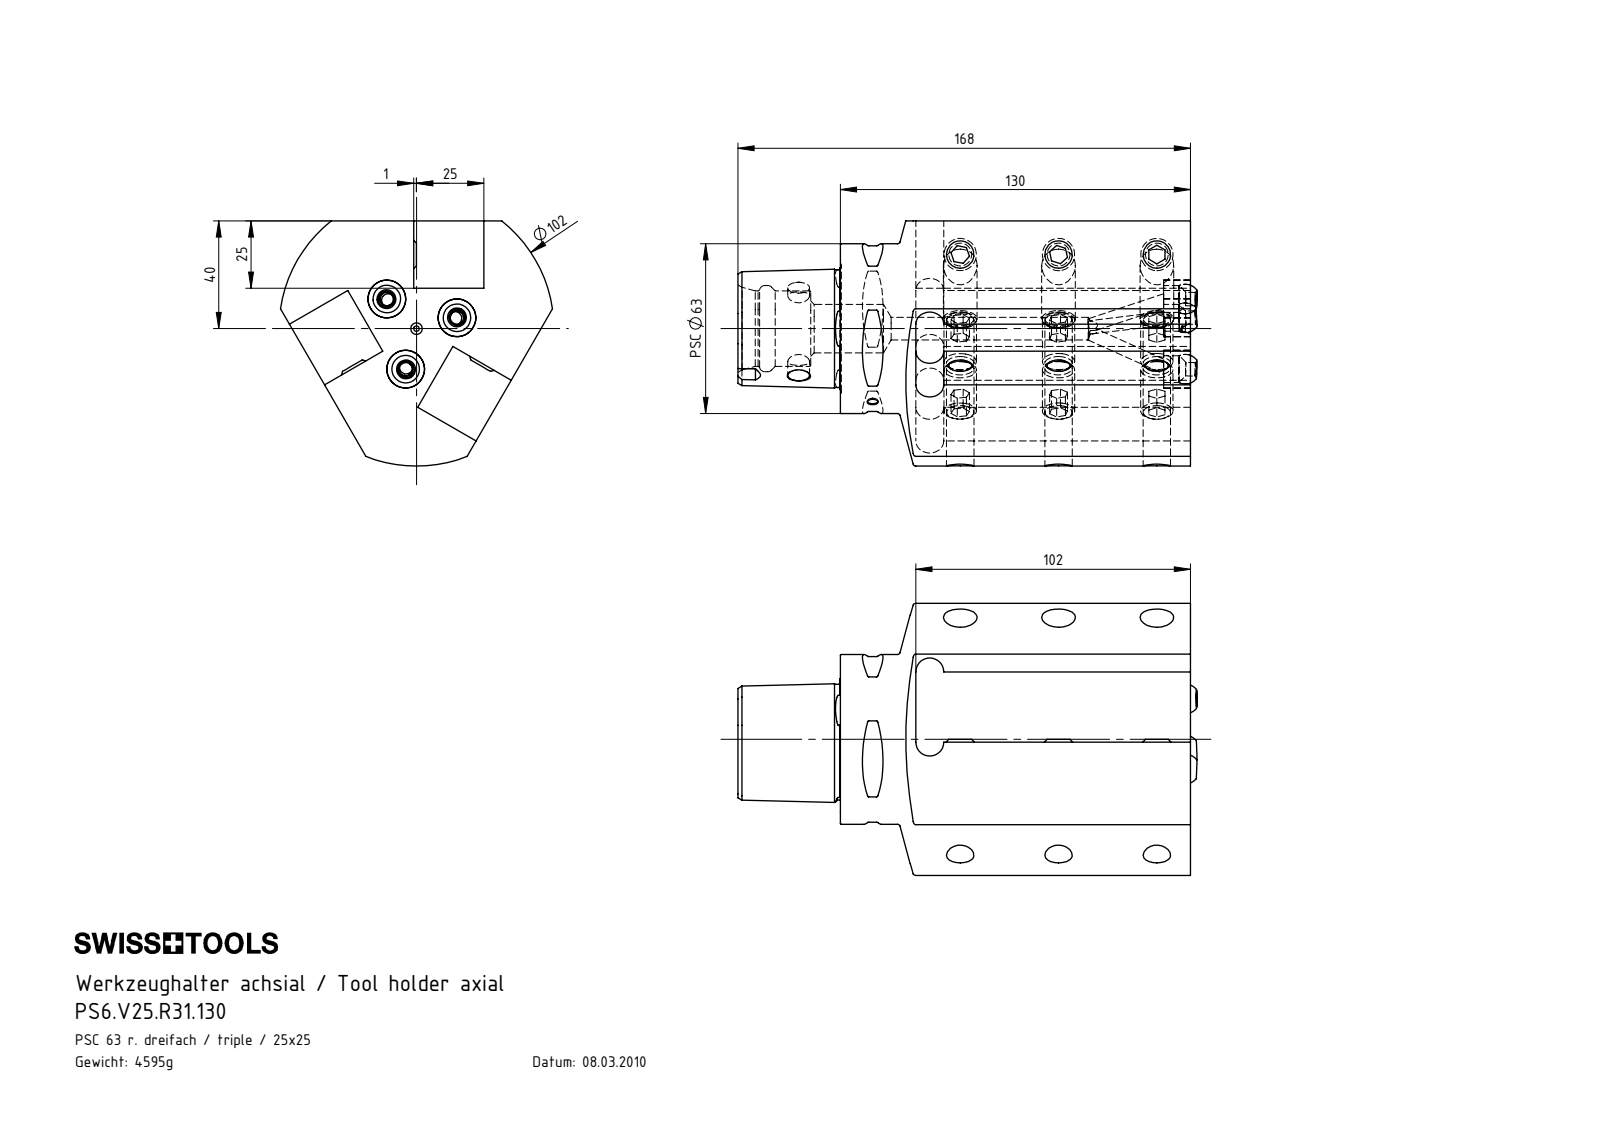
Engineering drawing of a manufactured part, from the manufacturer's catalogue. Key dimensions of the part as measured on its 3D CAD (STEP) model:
Part name (STEP PRODUCT): PS6-V25.R31.130_A; KU1-U14.001.012_1; PS6.V25.R31.130; KU1-U14.001.012 (+2 more)
STEP written by: SolidWorks 2017 (AUTOMOTIVE_DESIGN)
Units: millimetres
Bodies: 16 solids, 418 faces (127 planar, 126 cylindrical, 165 other)
Overall size (bounding box): 170.81 × 100.92 × 91
Volume: 581 513 mm³ · Surface area: 105 244 mm²
Round holes (diameter × count): ⌀10.2 ×9, ⌀12.5 ×9, ⌀5 ×6, ⌀10 ×3, ⌀14 ×3, ⌀2 ×1, ⌀4 ×1, ⌀8.1 ×1, ⌀8.4 ×1, ⌀18 ×1, ⌀28 ×1, ⌀32 ×1
Round bosses / shafts (diameter × count): ⌀12 ×9, ⌀63 ×1
Partial cylindrical surfaces — rounded edges, fillets, slot ends (radius × count): R0.5 ×8, R5.2 ×6, R6 ×1, R51 ×1
Main face-to-face distances: 25, 26, 102, 28, 130, 6, 120, 92, 10, 11
Hole centre spacings: 36.5, 15.56, 26.95, 73, 27.5, 42.57, 66, 74.28
